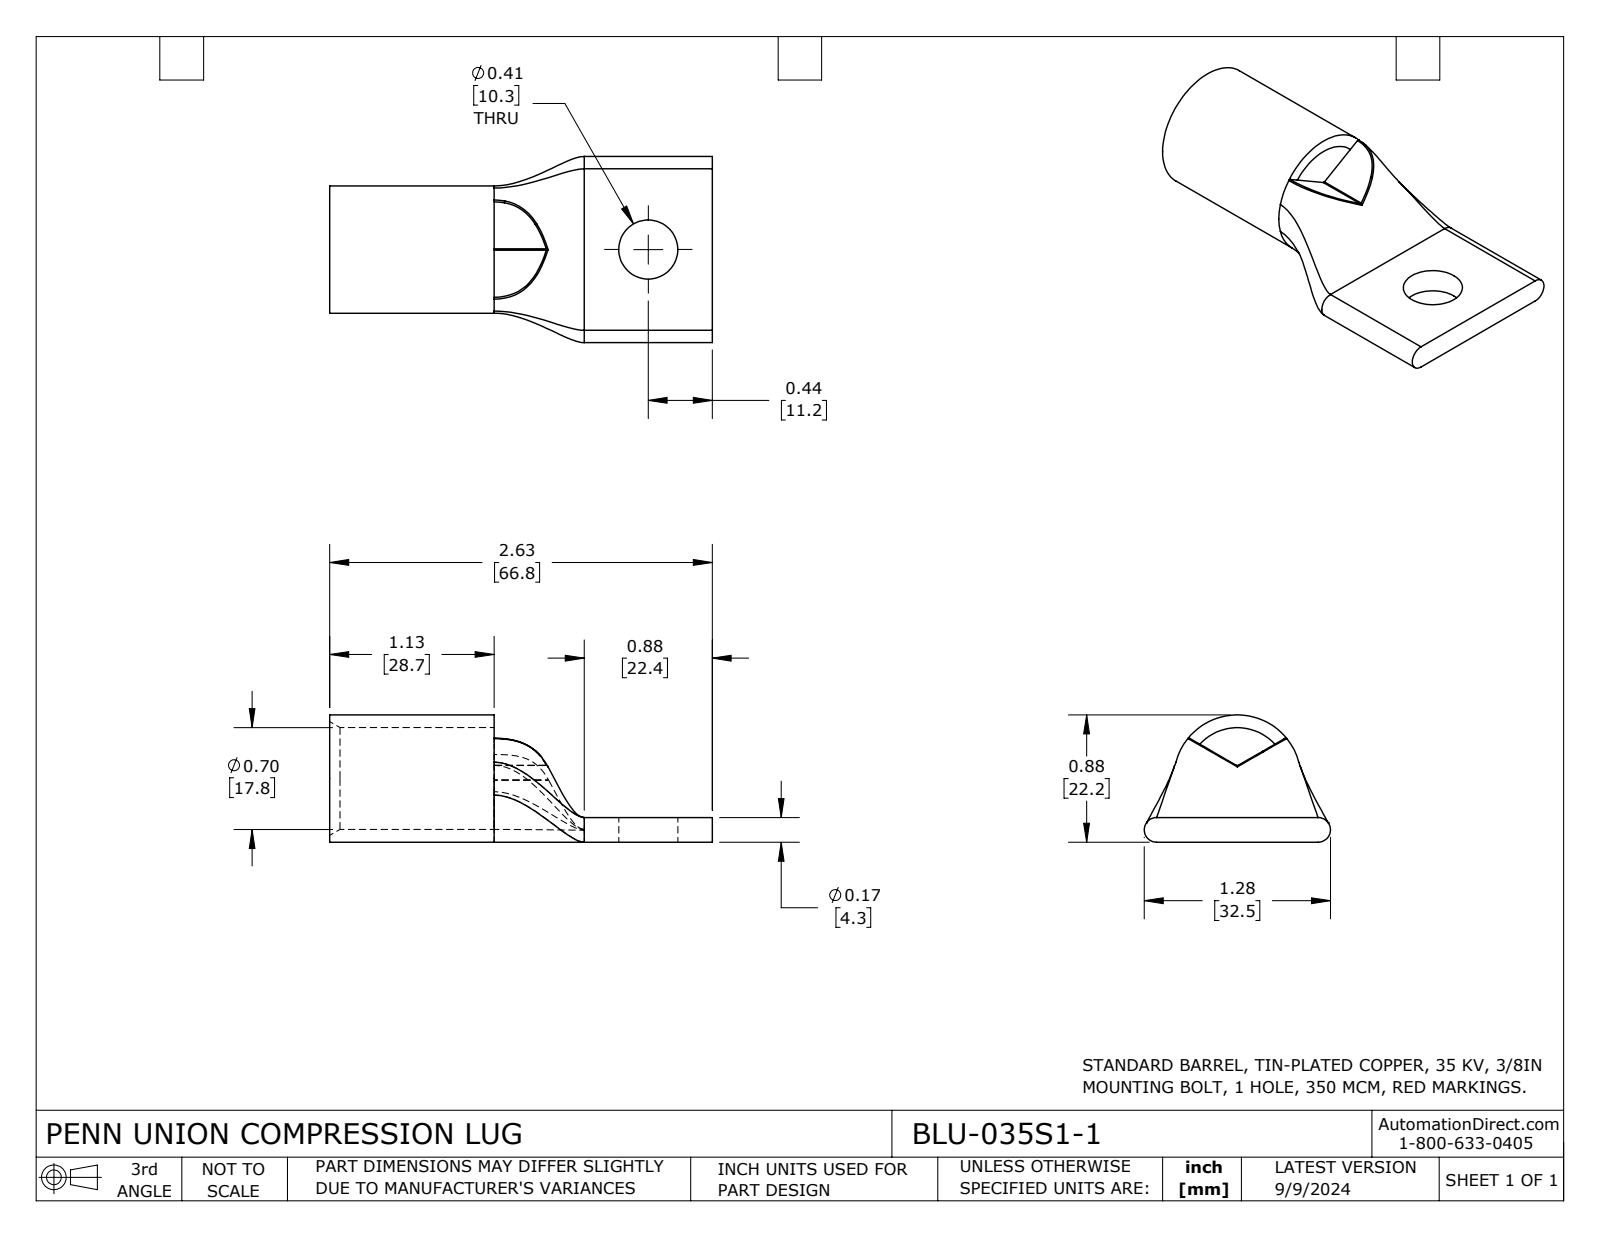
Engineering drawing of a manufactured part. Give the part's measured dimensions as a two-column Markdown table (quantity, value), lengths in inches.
| quantity | value |
| --- | --- |
| part name | BLU-035S1-1 |
| STEP written by | SolidWorks 2023 (CONFIG_CONTROL_DESIGN) |
| units | inches |
| bodies | 1 solid, 37 faces (11 planar, 11 cylindrical, 15 other) |
| overall size | 2.63 × 1.28 × 0.875 |
| volume | 0.529 in³ |
| surface area | 11.91 in² |
| round holes (diameter × count) | 0.406 × 1, 0.7 × 1 |
| round bosses / shafts (diameter × count) | 0.875 × 1 |
| partial cylindrical surfaces (radius × count) | 0.01 × 2, 0.085 × 2 |
| main face-to-face distances | 0.17, 0.087, 2.63, 1.13, 1.5, 1.75, 0.62, 0.88 |
